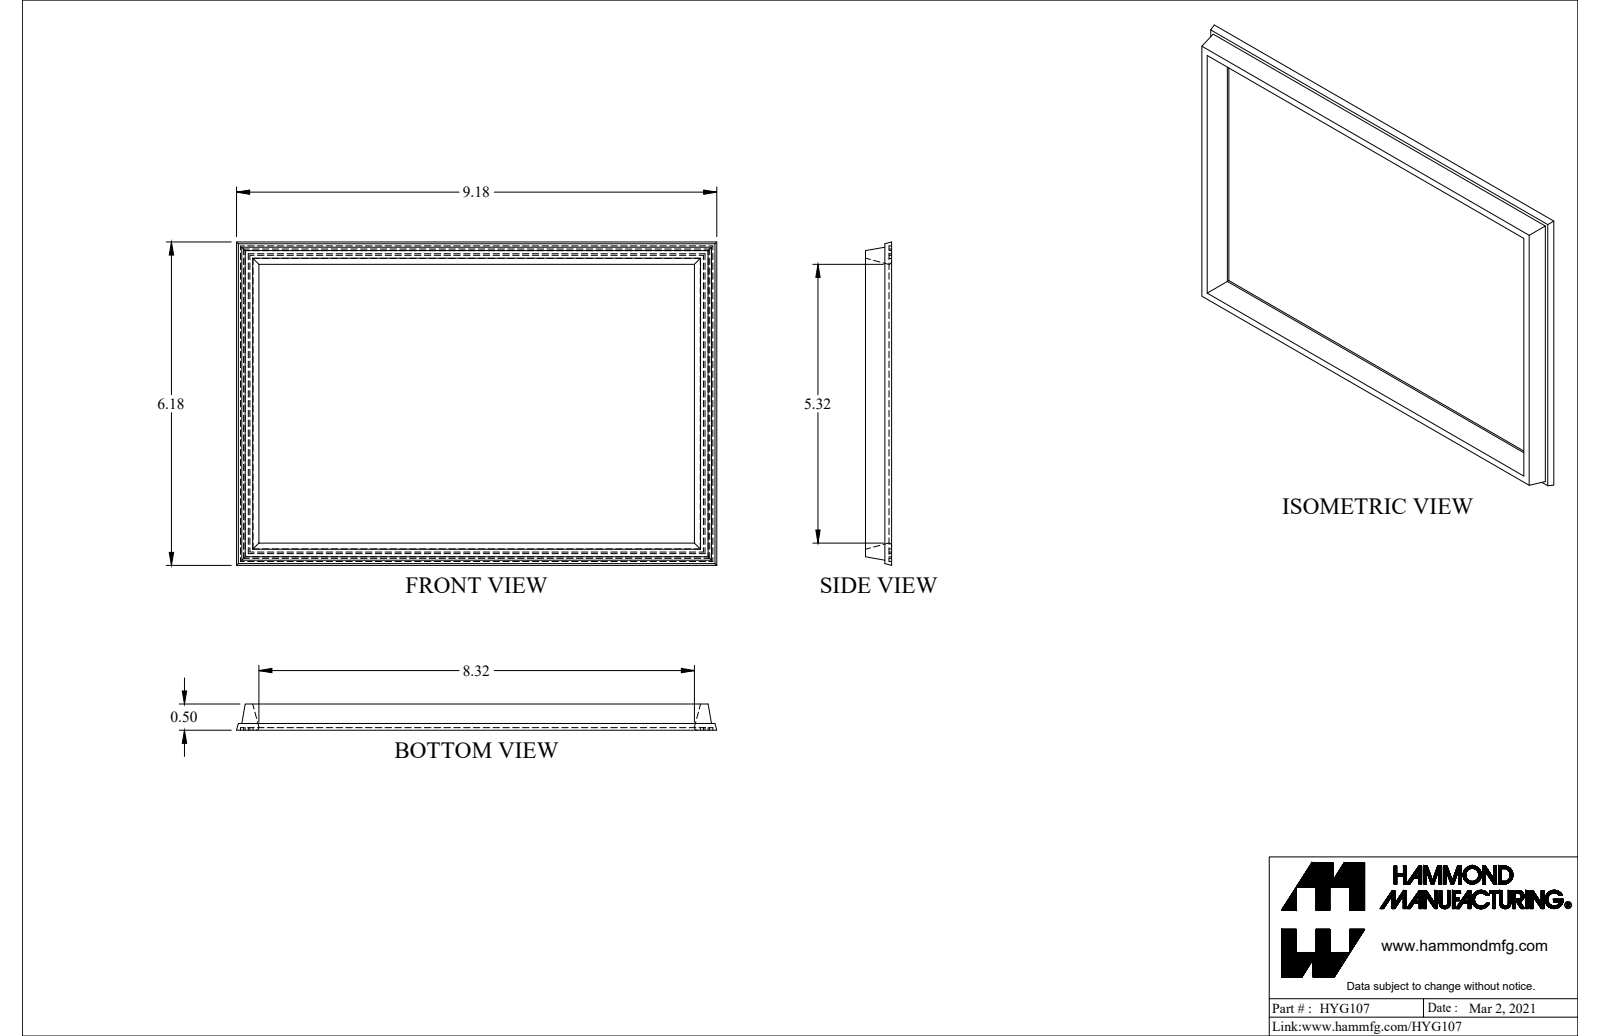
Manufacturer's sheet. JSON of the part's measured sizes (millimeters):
{"part_name": "HYG107", "step_written_by": "SolidWorks 2021 (AUTOMOTIVE_DESIGN)", "units": "millimeters", "bodies": {"solids": 1, "faces": 49, "planar": 45, "cylindrical": 4, "other": 0}, "overall_size": [233.1, 156.9, 12.7], "volume_mm3": 59730, "surface_area_mm2": 36210, "partial_cylinders_radius": [[1.4, 4]], "face_to_face_distances": [1.3, 12.7, 11.4, 2.3, 1.5, 3.8, 147, 140.7, 0.8, 2.3]}
